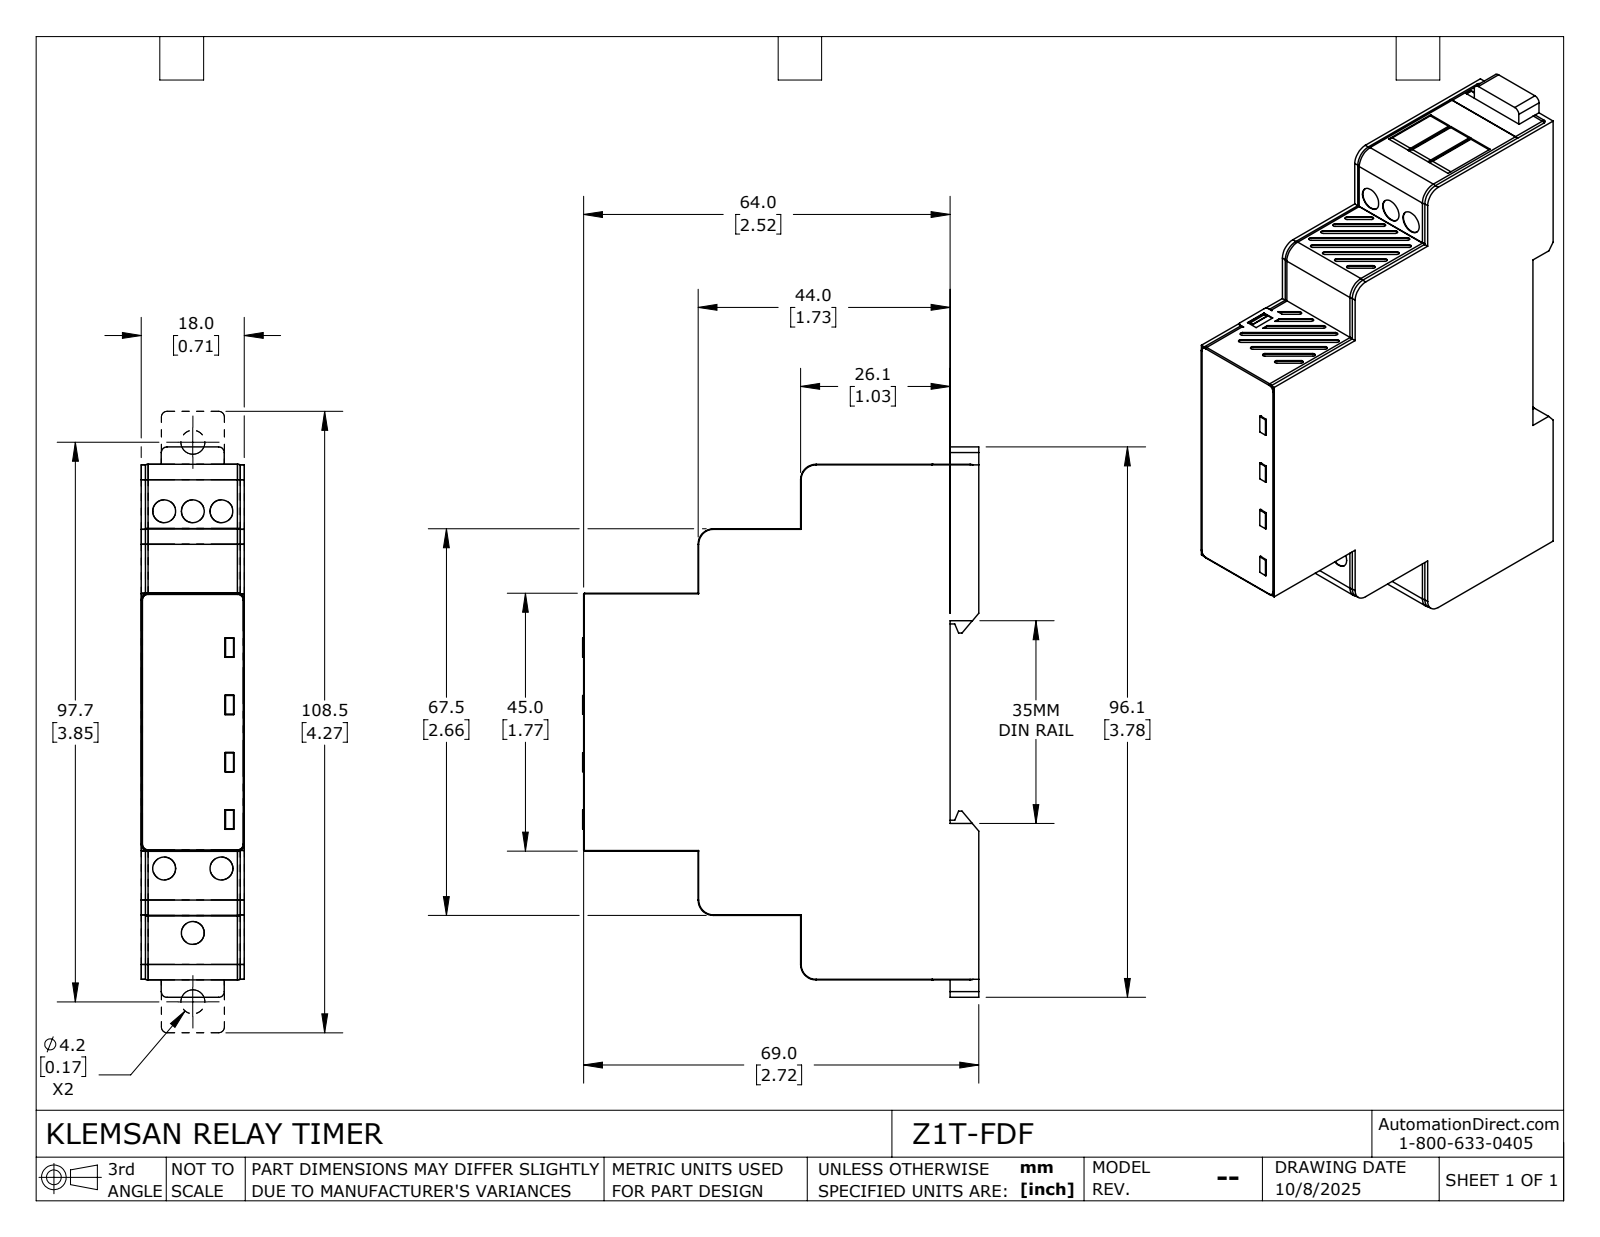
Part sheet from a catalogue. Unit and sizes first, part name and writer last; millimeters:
Units: millimetres
Overall size (bounding box): 96.07 × 69.15 × 18
Round holes (diameter × count): ⌀4.2 ×2, ⌀4 ×1
Partial cylindrical surfaces — rounded edges, fillets, slot ends (radius × count): R1.2 ×16, R0.2 ×4, R1 ×4, R2.6 ×4, R2.7 ×4, R0.5 ×2, R1.5 ×2
Main face-to-face distances: 18, 3.5, 14.5, 11.25, 64, 5, 69, 22.5, 67.4, 67.5
Hole centre spacings: 5.83, 79.43, 85.26
Volume: 83 847 mm³ · Surface area: 17 884 mm²
Bodies: 3 solids, 440 faces (280 planar, 60 cylindrical, 100 other)
Part name (STEP PRODUCT): Z1T-FDF
STEP written by: SolidWorks 2024 (CONFIG_CONTROL_DESIGN)
